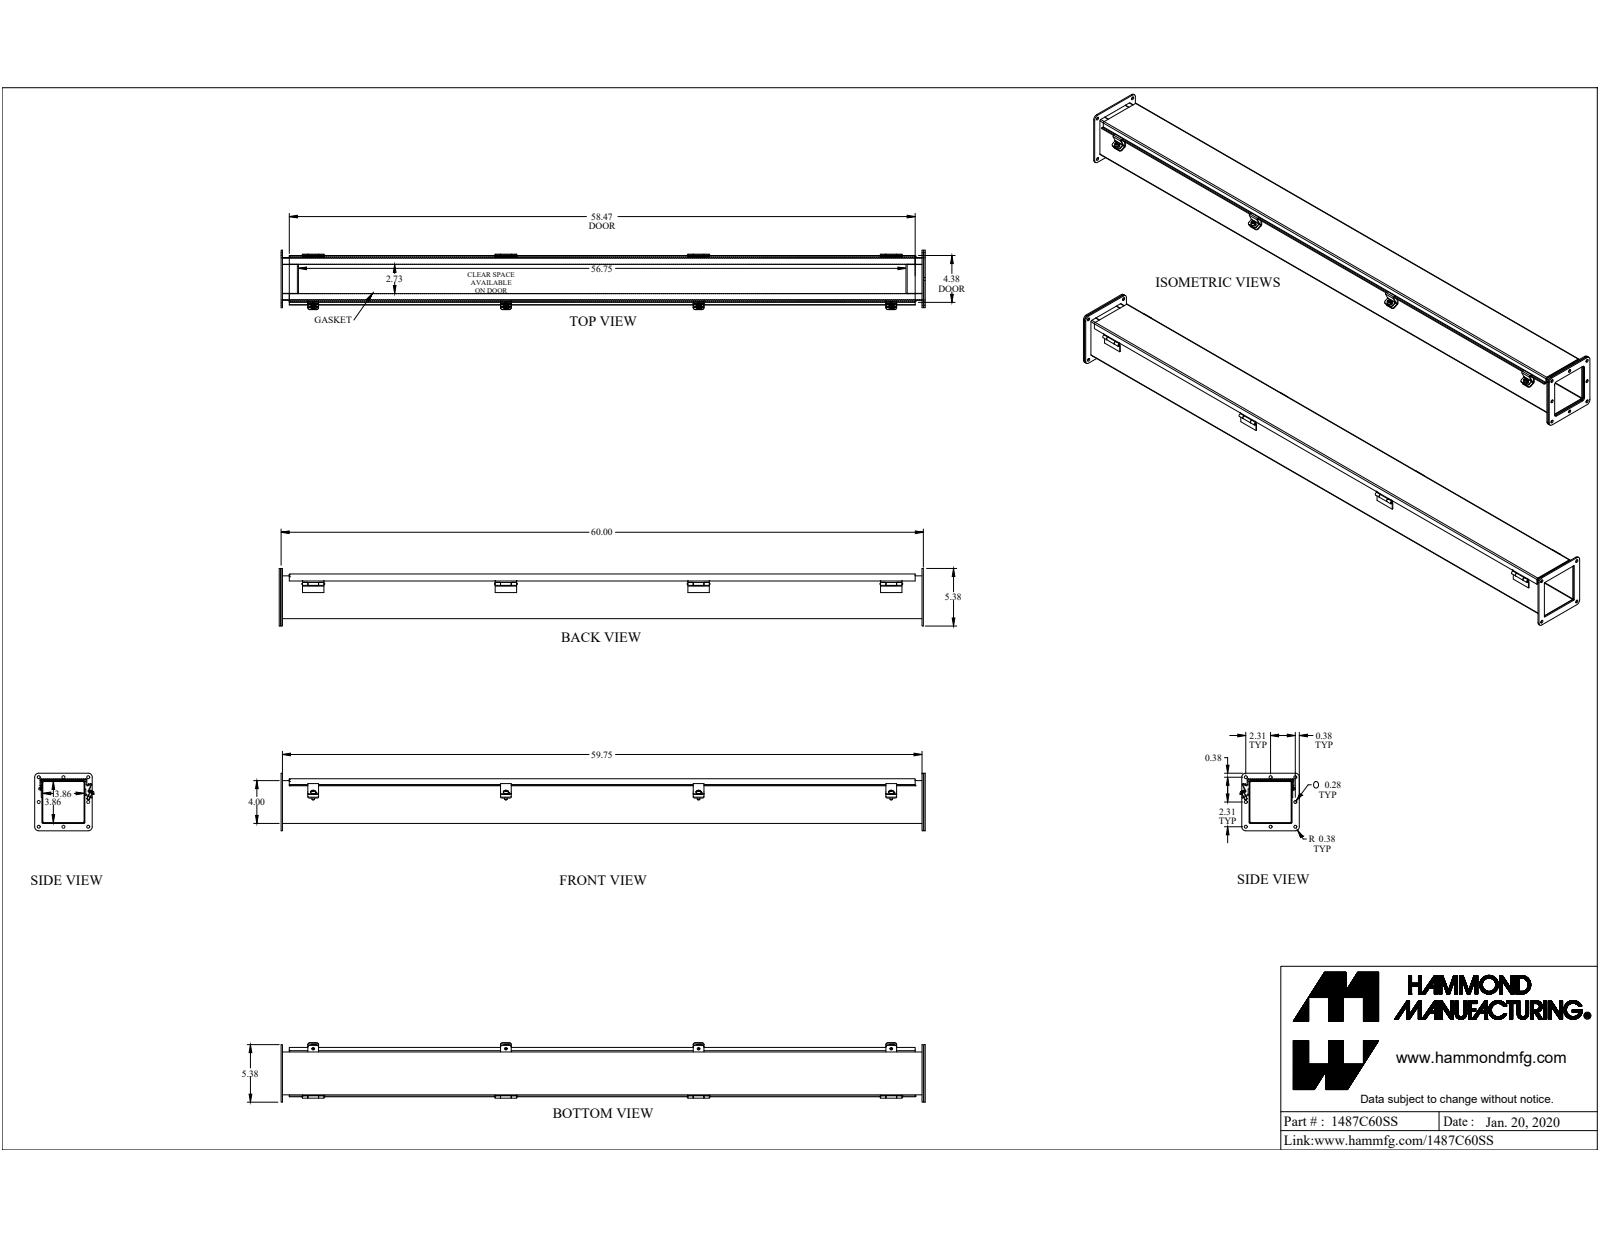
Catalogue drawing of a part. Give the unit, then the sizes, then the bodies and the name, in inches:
Units: inches
Overall size (bounding box): 60.546 × 5.552 × 5.375
Round holes (diameter × count): ⌀0.281 ×8, ⌀0.213 ×4, ⌀0.187 ×1, ⌀0.196 ×1, ⌀0.258 ×1, ⌀0.35 ×1
Round bosses / shafts (diameter × count): ⌀0.25 ×5, ⌀0.48 ×4, ⌀0.5 ×1, ⌀0.337 ×1, ⌀0.18 ×1
Partial cylindrical surfaces — rounded edges, fillets, slot ends (radius × count): R0.188 ×16, R0.03 ×8, R0.141 ×8, R0.375 ×8, R0.036 ×7, R0.108 ×7, R0.02 ×6, R0.062 ×4
Main face-to-face distances: 0.072, 3.928, 4.1, 4, 3.856, 4.172, 4.028, 0.187, 0.259, 0.172
Hole centre spacings: 2.313, 5.171, 4.625, 4.625, 18, 2.312, 3.27, 3.27
Volume: 104.7 in³ · Surface area: 2 654 in²
Bodies: 39 solids, 786 faces (508 planar, 208 cylindrical, 70 other)
Part name (STEP PRODUCT): 1487C60SS
STEP written by: SolidWorks 2019 (CONFIG_CONTROL_DESIGN)
